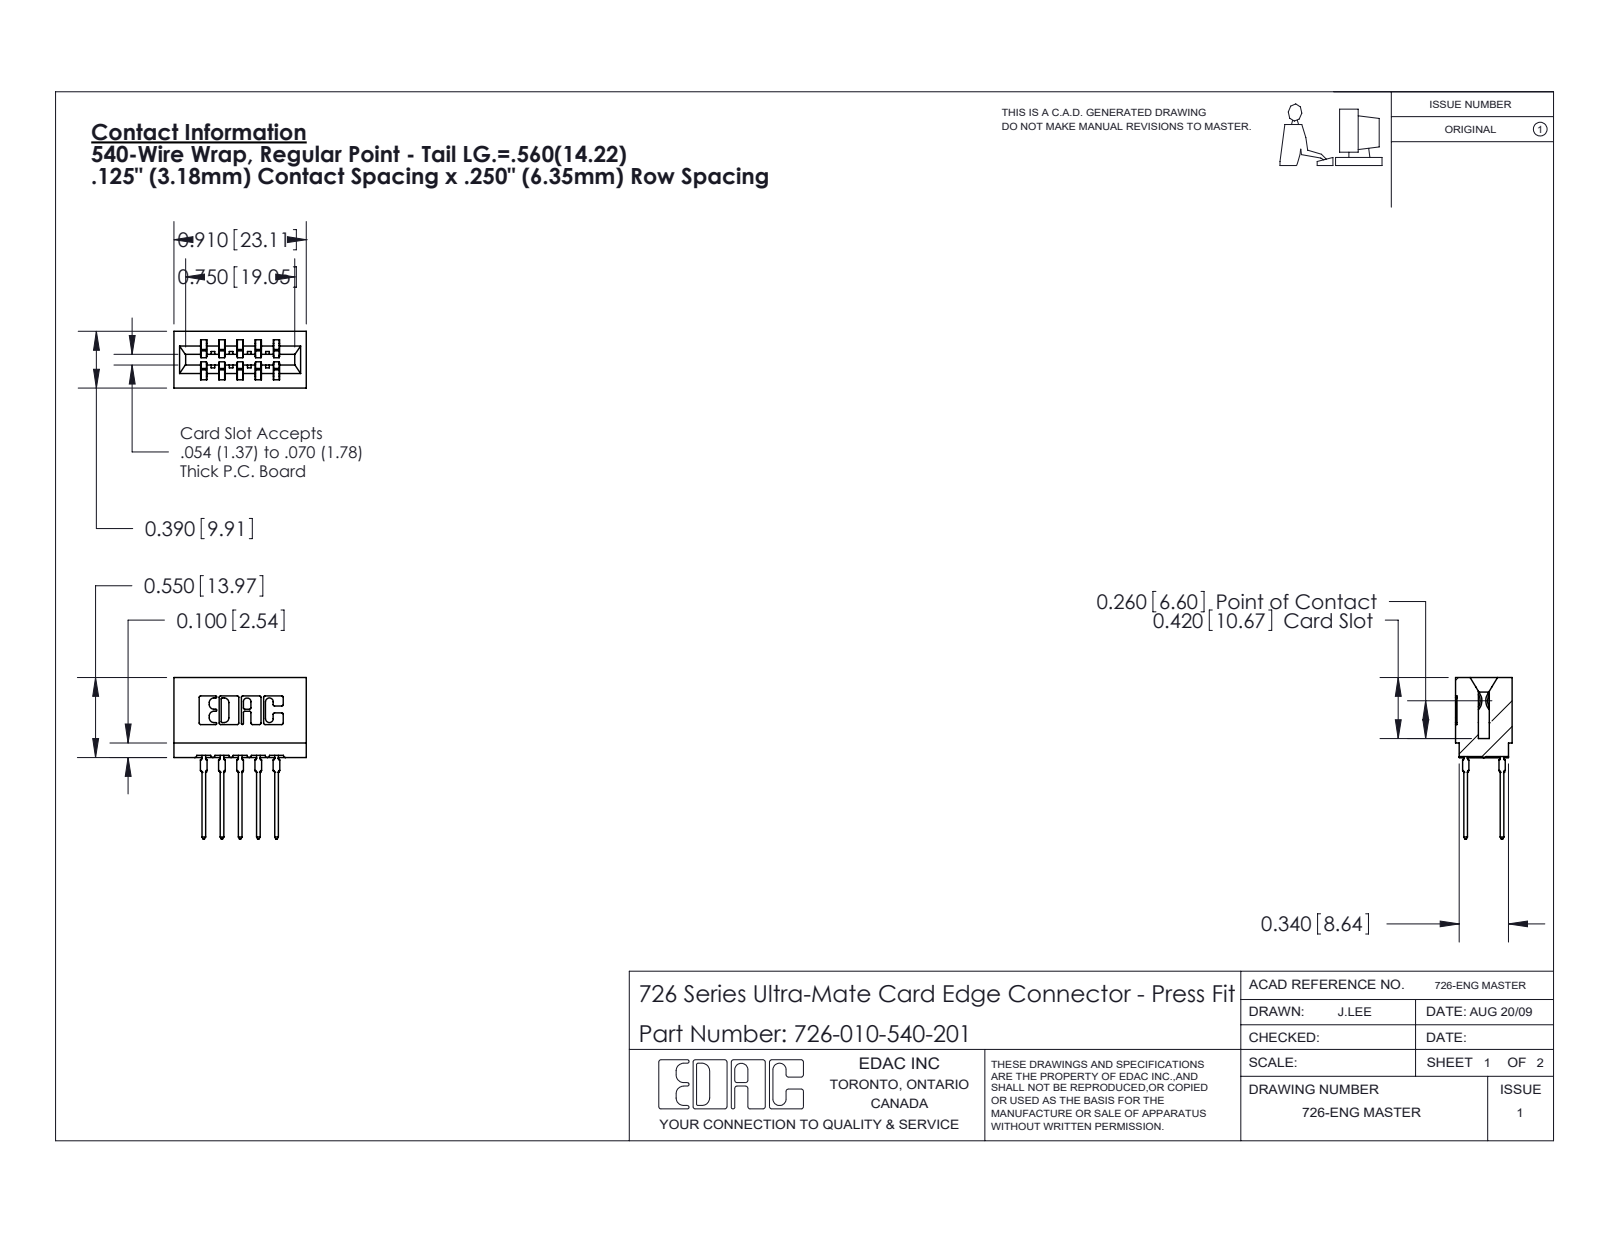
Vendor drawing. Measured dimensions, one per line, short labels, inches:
name: 726 Part_.515 Slot Depth - 01; 746-292-001_540; 726-010-540-201
written by: SolidWorks 2020 (CONFIG_CONTROL_DESIGN)
unit: in
bodies: 11 solids, 992 faces (515 planar, 217 cylindrical, 260 other)
size: 1.109 × 0.91 × 0.39
volume: 0.144 in³; area: 5.278 in²
rounds: 22× R0.01, 20× R0.021, 8× R0.005, 8× R0.011, 6× R0.007, 6× R0.015, 6× R0.031, 3× R0.026
face distances: 0.25, 0.057, 0.333, 0.042, 0.125, 0.125, 0.025, 0.083, 0.307, 0.39
